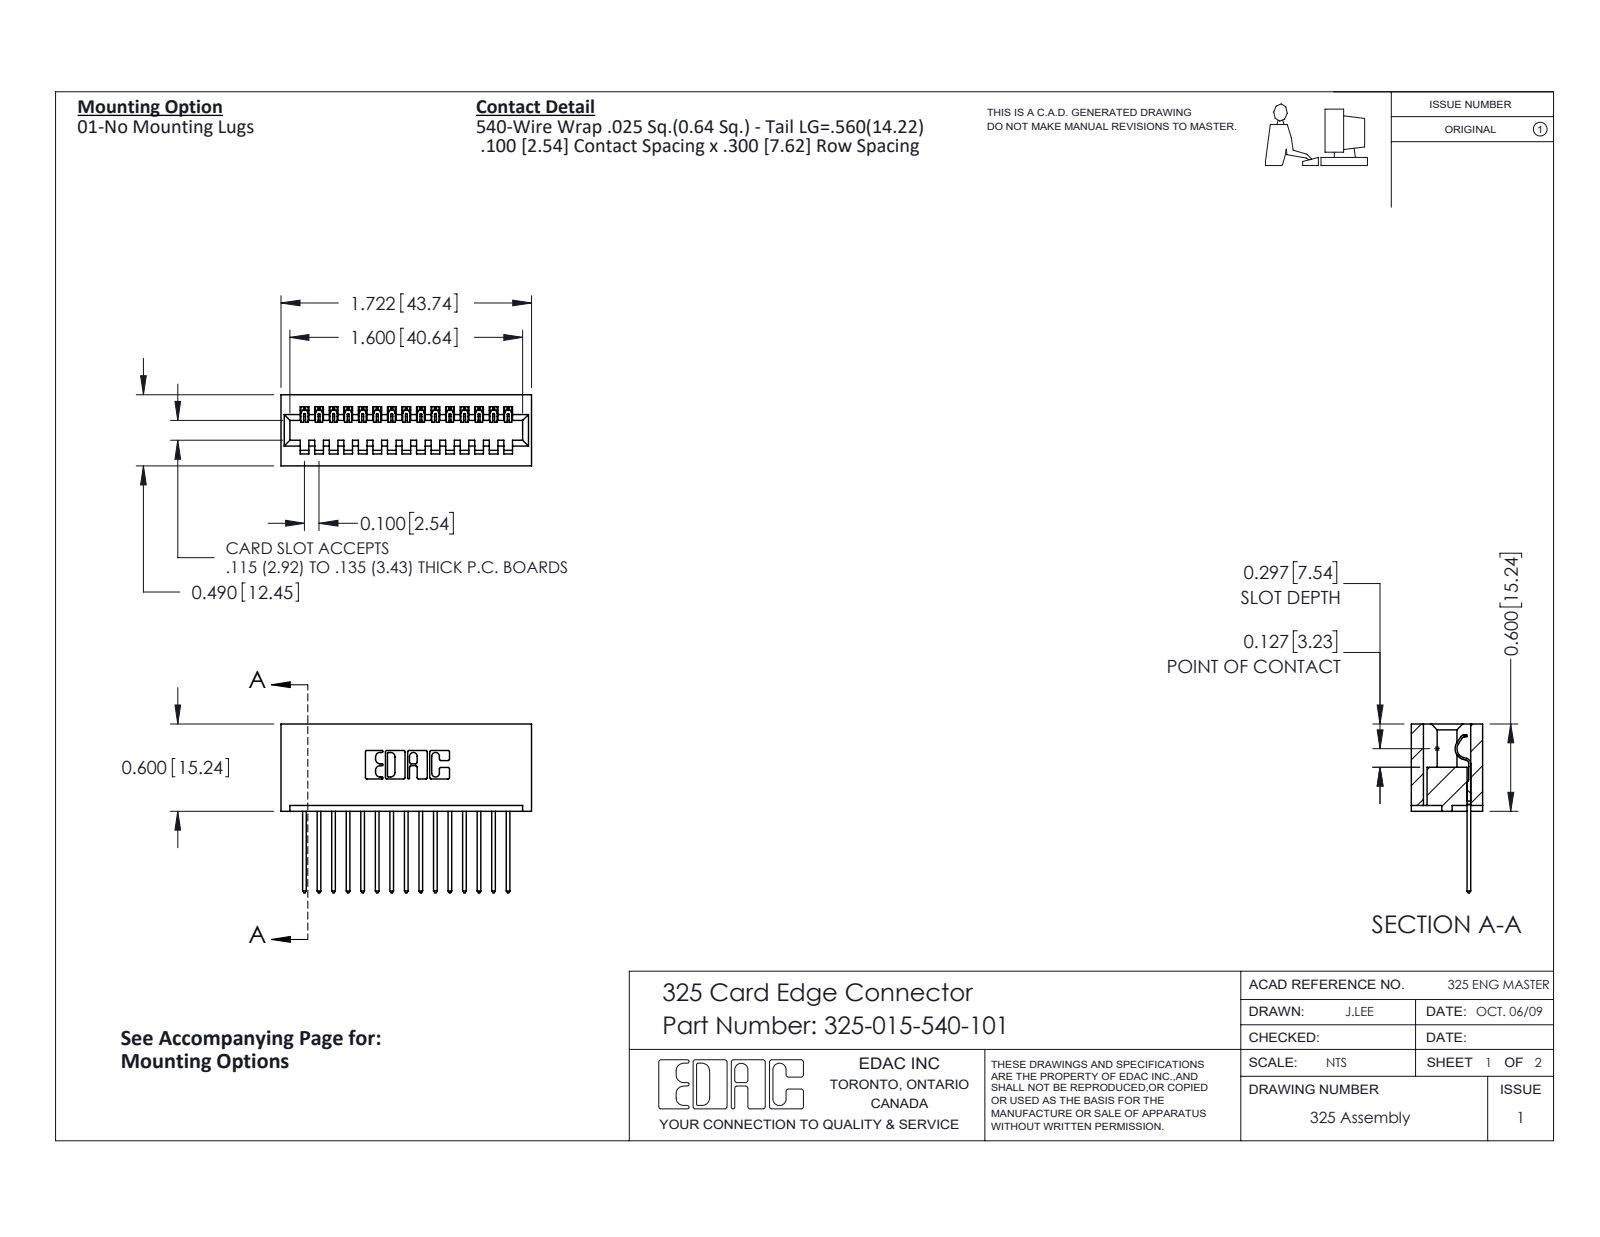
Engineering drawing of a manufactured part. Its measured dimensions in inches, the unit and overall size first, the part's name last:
Units: inches
Overall size (bounding box): 1.722 × 1.16 × 0.49
Partial cylindrical surfaces — rounded edges, fillets, slot ends (radius × count): R0.006 ×30, R0.01 ×30, R0.01 ×22, R0.007 ×6, R0.031 ×6, R0.026 ×3, R0.014 ×1, R0.022 ×1
Main face-to-face distances: 0.083, 0.3, 0.407, 0.49, 0.1, 0.107, 0.383, 0.025, 0.2, 0.4
Volume: 0.362 in³ · Surface area: 10.33 in²
Bodies: 16 solids, 976 faces (696 planar, 280 cylindrical, 0 other)
Part name (STEP PRODUCT): 325 Part_Lugless; 325-292-001_325-293-140; 325-015-540-101
STEP written by: SolidWorks 2016 (CONFIG_CONTROL_DESIGN)
